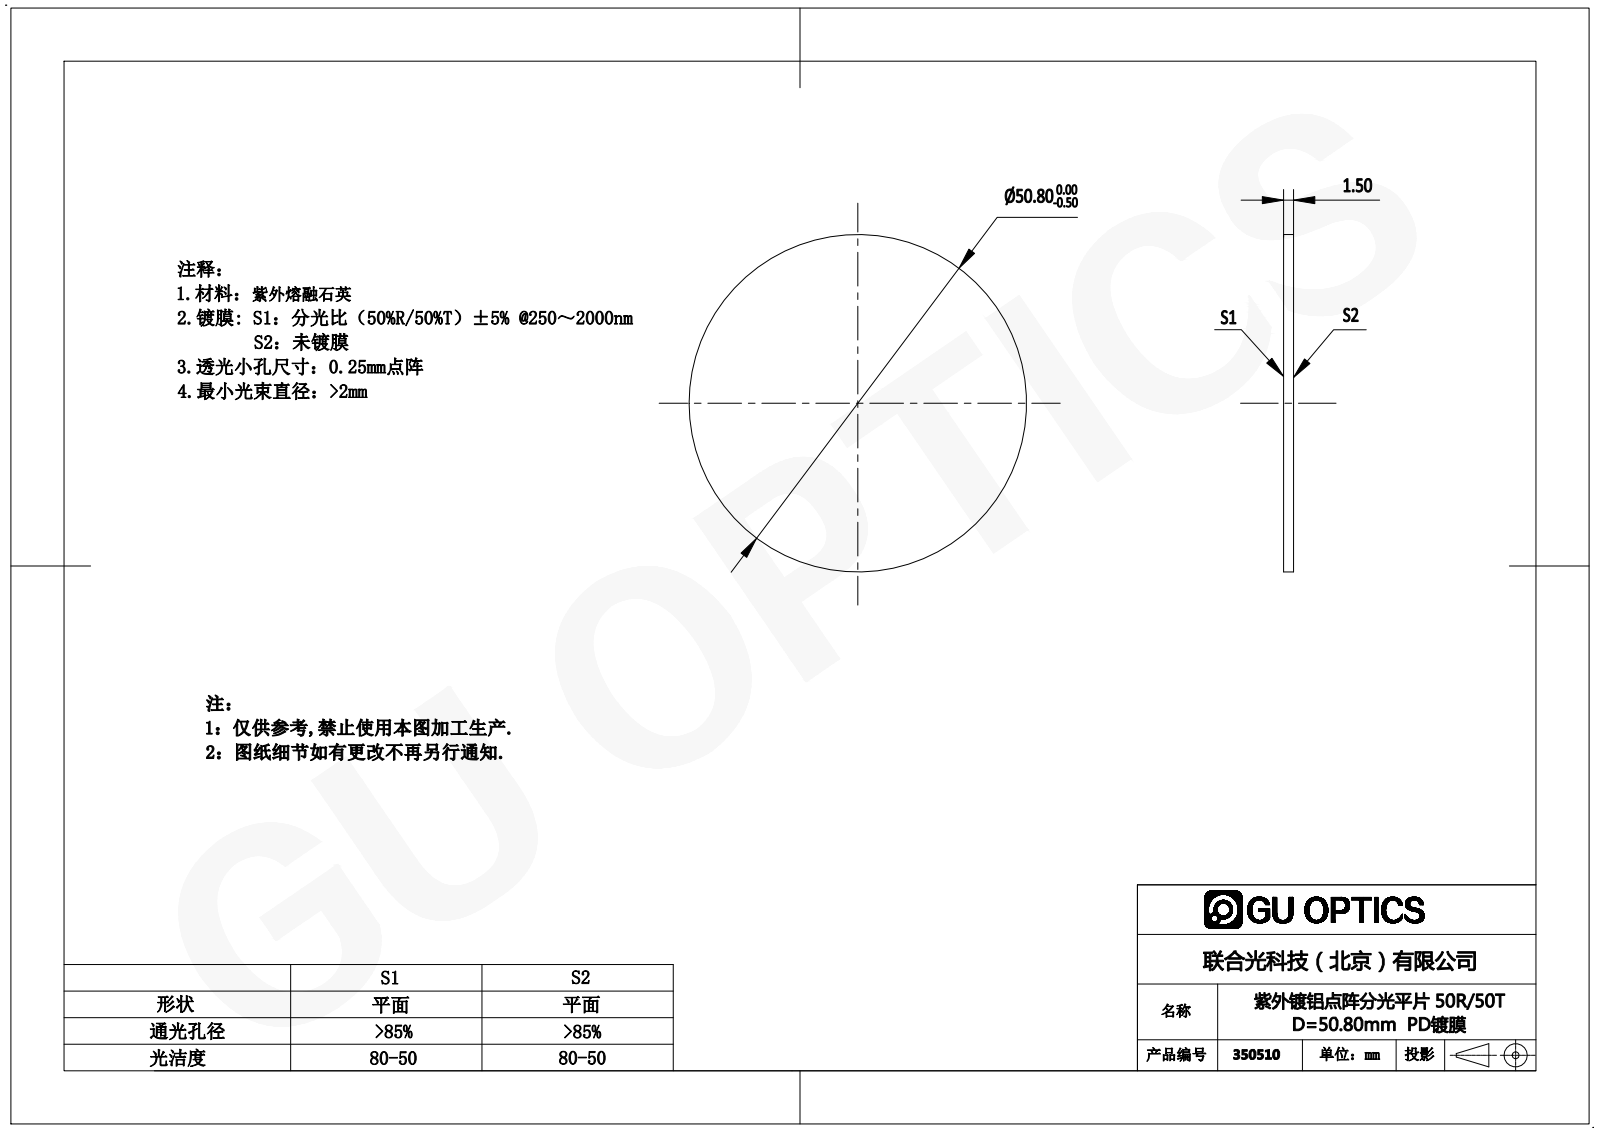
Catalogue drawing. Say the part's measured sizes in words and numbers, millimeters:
The part is named "350504". Its 3-D file was written by "SolidWorks 2016 (AUTOMOTIVE_DESIGN)". It is 1 solid with 4 faces: 2 planar, 2 cylindrical and 0 other. Overall it measures 50.8 by 50.8 by 1.5 millimeters. Its volume is 3 040 cubic millimeters and its surface area 4 293 square millimeters. Round bosses or shafts: 1 of diameter 50.8. The main face-to-face distances are 1.5.
